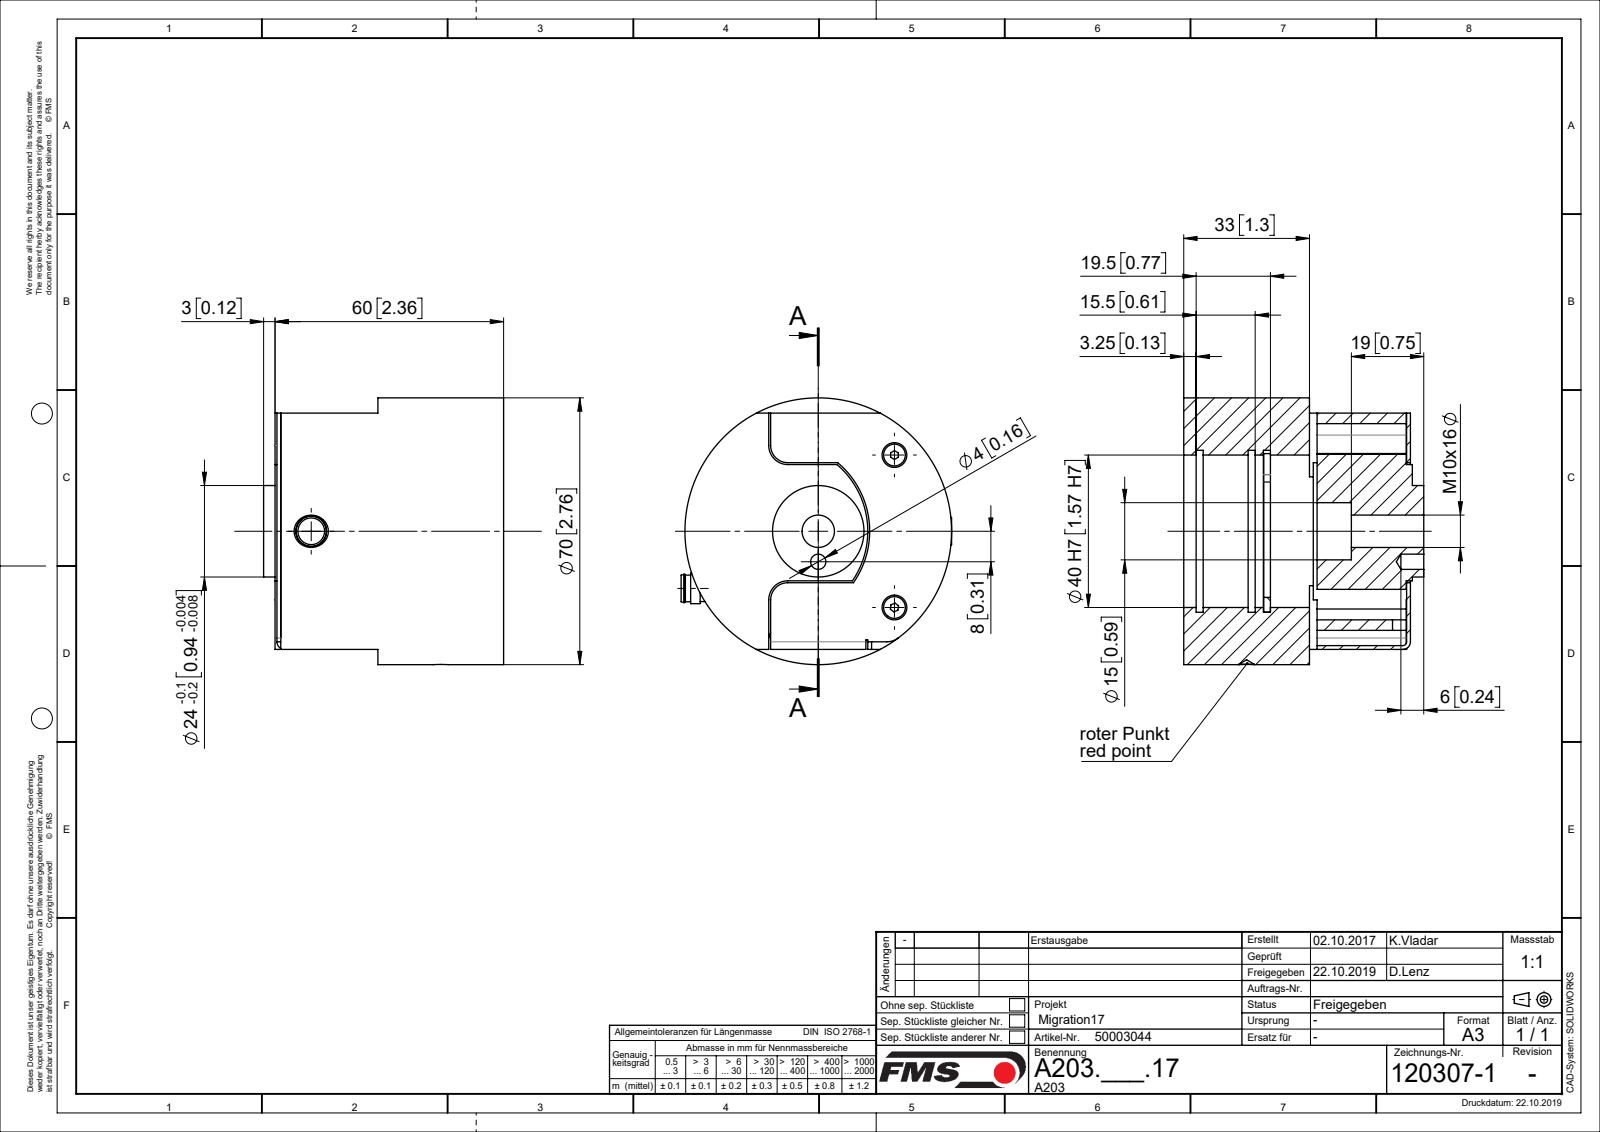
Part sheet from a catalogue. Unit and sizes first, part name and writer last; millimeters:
Units: millimetres
Overall size (bounding box): 71 × 70 × 63
Round holes (diameter × count): ⌀2.6 ×2, ⌀4 ×2, ⌀5 ×1, ⌀5.7 ×1, ⌀5.8 ×1, ⌀7.8 ×1, ⌀8 ×1, ⌀8.68 ×1, ⌀15 ×1, ⌀40 ×1, ⌀42.5 ×1
Round bosses / shafts (diameter × count): ⌀1 ×4, ⌀6 ×2, ⌀3 ×2, ⌀70 ×1, ⌀24 ×1, ⌀8 ×1, ⌀7.5 ×1, ⌀7.4 ×1
Partial cylindrical surfaces — rounded edges, fillets, slot ends (radius × count): R5 ×4, R2 ×3, R4.5 ×2, R1 ×1, R10 ×1, R23 ×1, R23.5 ×1
Main face-to-face distances: 1, 58.5, 23.5, 35, 25.5, 24.5, 26.5, 33, 2, 59.5
Hole centre spacings: 28.28, 8, 15.3, 23.32, 34.41, 40
Volume: 171 573 mm³ · Surface area: 38 083 mm²
Bodies: 6 solids, 212 faces (77 planar, 85 cylindrical, 50 other)
Part name (STEP PRODUCT): C1203071; C1203072; C1111073; SENKSCHRAUBE_I-6KT_M3X5 (+3 more)
STEP written by: Mechanical Desktop 2009 (CONFIG_CONTROL_DESIGN)
